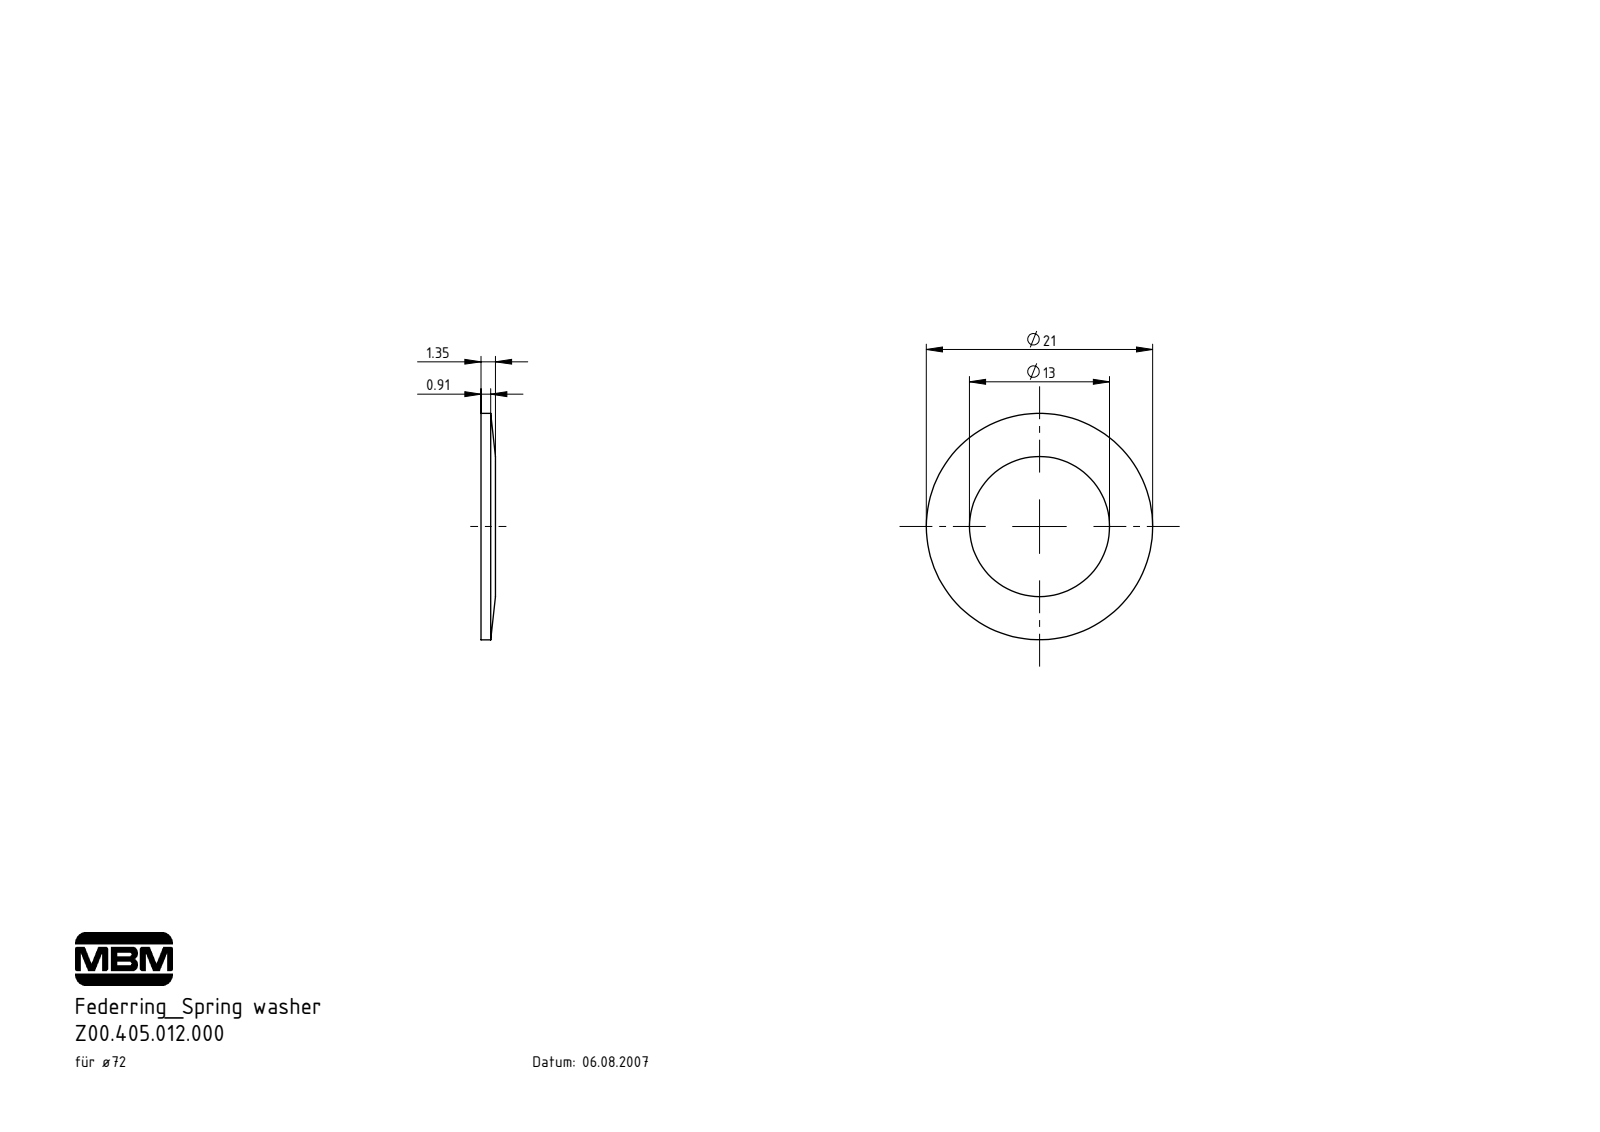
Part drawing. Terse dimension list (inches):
name: Z00.405.012.000
written by: SolidWorks 2022 (AUTOMOTIVE_DESIGN)
unit: in
bodies: 1 solid, 6 faces (2 planar, 4 cylindrical, 0 other)
size: 0.827 × 0.827 × 0.035
volume: 0.012 in³; area: 0.811 in²
holes: 1× ⌀0.512
bosses: 1× ⌀0.827
face distances: 0.035
